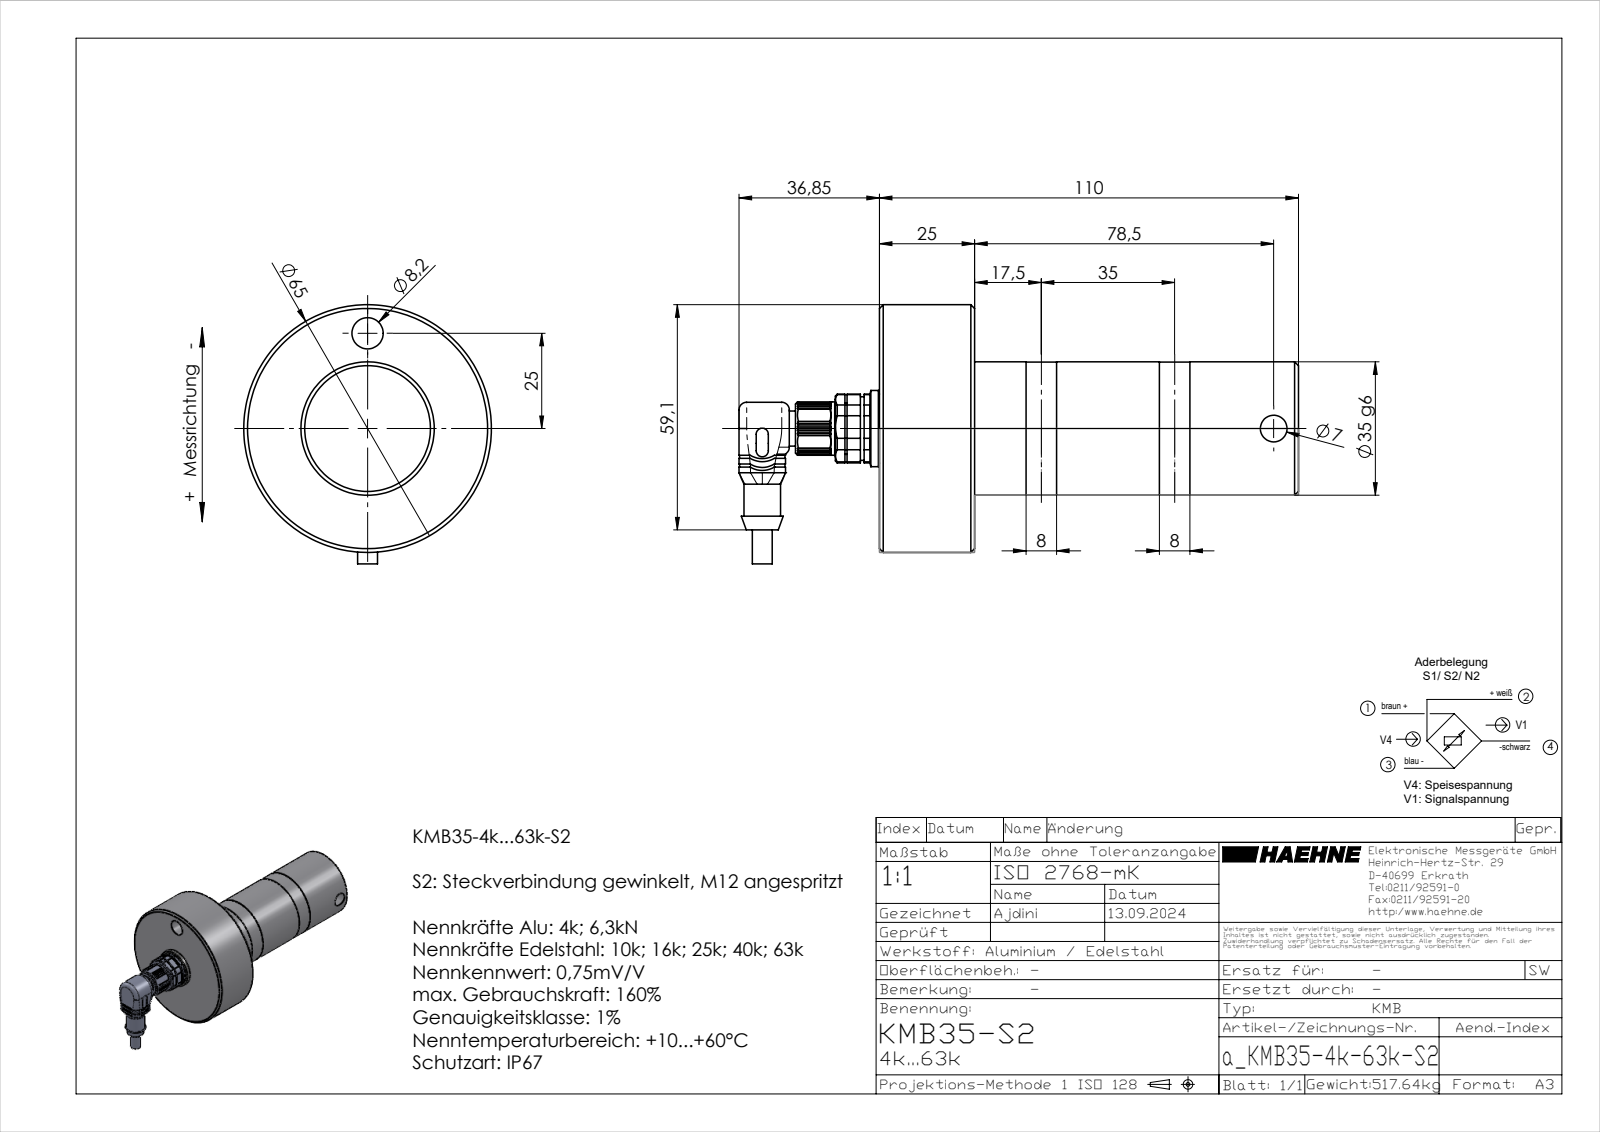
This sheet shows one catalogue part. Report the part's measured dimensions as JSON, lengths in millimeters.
{"part_name": "a_KMB35-4k-63k-S2; X02295Z1 Kabelbuchse gewinkelt M12 (HoTec); X02163Z1 Einschraubstecker M16x1,5 EC-FSD4-0,5_16 8027469(2); Option S2", "step_written_by": "SolidWorks 2023 (CONFIG_CONTROL_DESIGN)", "units": "millimeters", "bodies": {"solids": 4, "faces": 723, "planar": 386, "cylindrical": 190, "other": 147}, "overall_size": [146.85, 68.02, 65], "volume_mm3": 165494, "surface_area_mm2": 31190, "round_holes": [[0.67, 5], [1.1, 4], [1.15, 4], [1.6, 4], [1.85, 4], [1.2, 1], [7, 1], [8.2, 1], [8.37, 1], [8.42, 1], [9.3, 1], [10.16, 1]], "round_bosses_or_shafts": [[1.8, 4], [1.55, 4], [1.5, 4], [1, 4], [65, 1], [35, 1], [34.9, 1], [20, 1]], "partial_cylinders_radius": [[0.2, 16], [0.3, 9], [0.4, 4], [0.53, 4], [1, 4], [1.27, 4], [6, 4], [1.6, 2]], "face_to_face_distances": [25, 85, 110, 2.5, 9.05, 27.5, 3, 112.5, 121.55, 36.55], "hole_center_spacings": [1.14, 2.5, 3.54, 0.7, 0.71, 4.52, 5, 5.22]}
